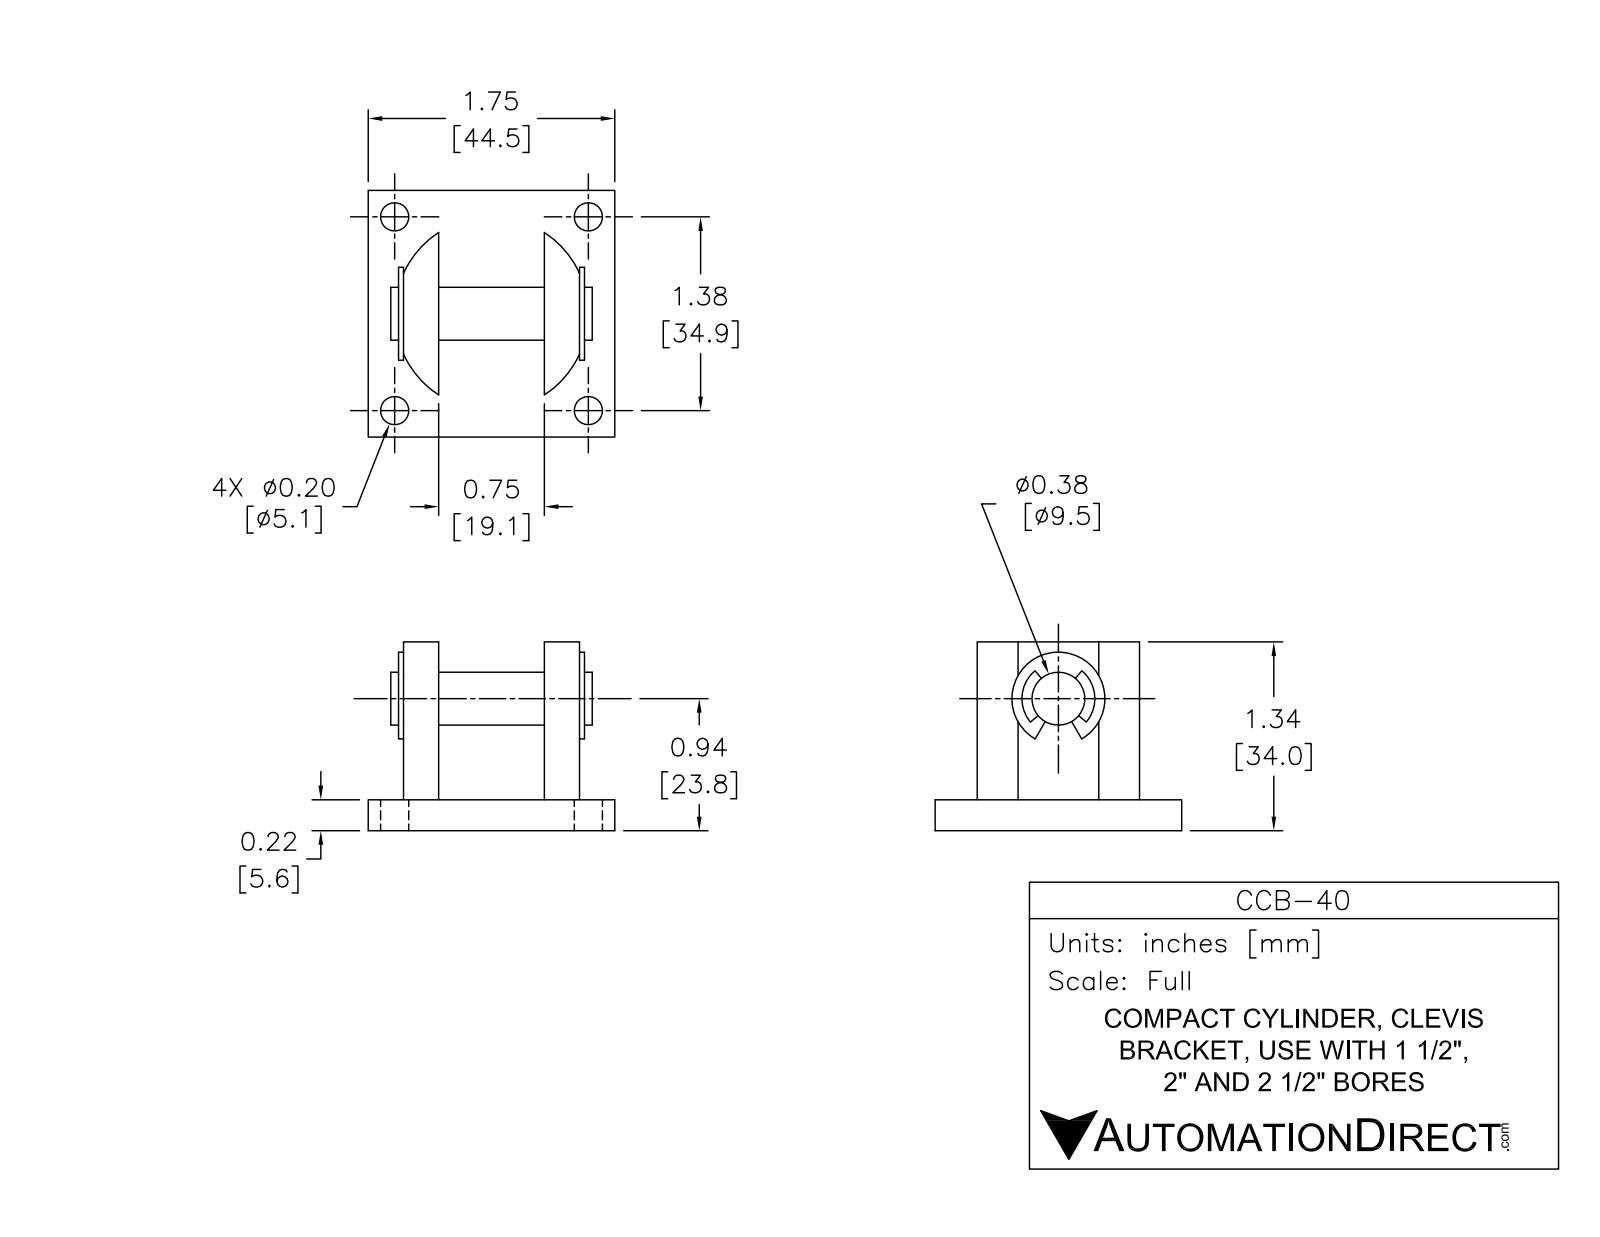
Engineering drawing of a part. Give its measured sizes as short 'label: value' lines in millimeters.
name: CCB-40_bracket; CCB-40; CCB-40-rr; CCB-40_pin
written by: SolidWorks 2014 (AUTOMOTIVE_DESIGN)
unit: mm
bodies: 4 solids, 95 faces (36 planar, 55 cylindrical, 4 other)
size: 44.5 × 44.5 × 34
volume: 20 940 mm³; area: 10 700 mm²
holes: 4× ⌀5.6, 1× ⌀9.7
bosses: 1× ⌀9.5, 1× ⌀7.7
rounds: 4× R0.4, 2× R0.8, 2× R1.5, 1× R3.9, 1× R6.1, 1× R8.4, 1× R17.4, 1× R17.5
face distances: 5.6, 6.4, 19.1, 31.8, 12.7, 44.5, 38.1, 25.4, 34, 28.4
hole spacings: 35.1, 49.6
